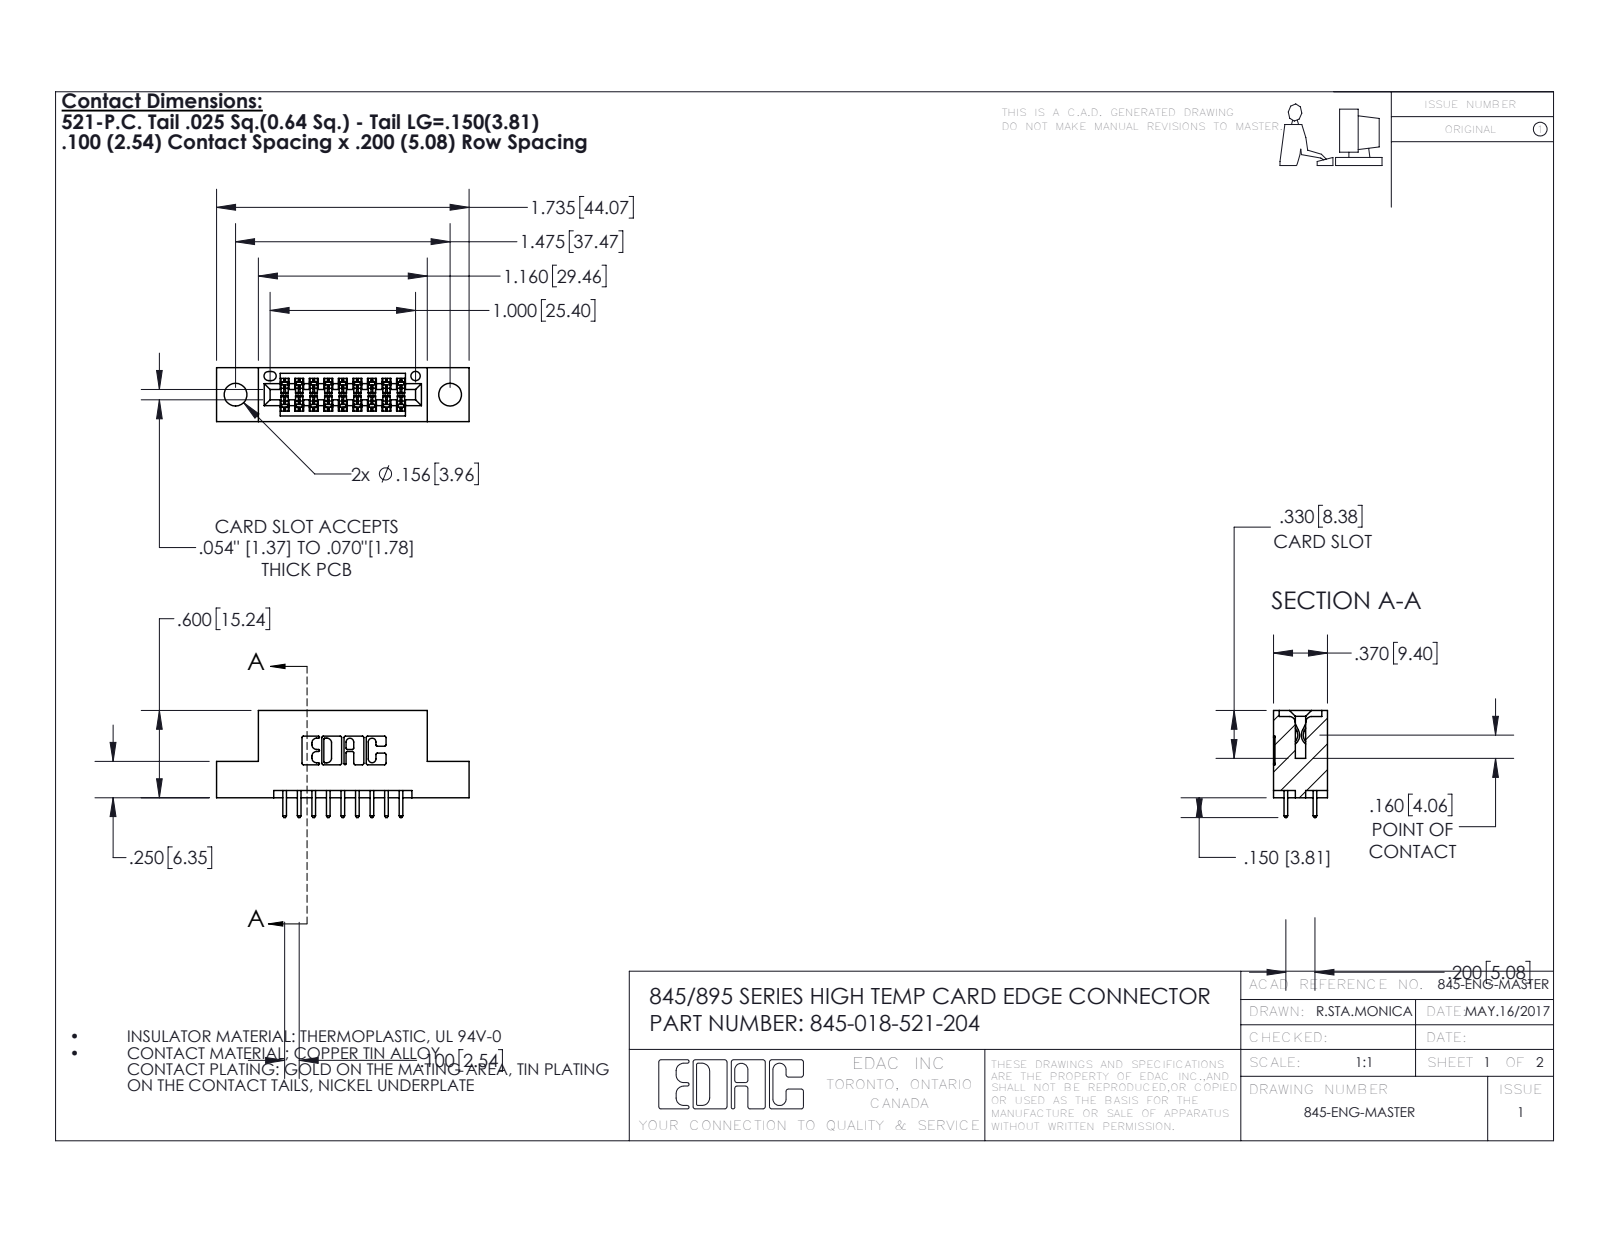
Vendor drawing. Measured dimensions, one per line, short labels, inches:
name: 345-292-001_345-293-121; 345-018-521-204; 345 Part_Flush Mounting Lugs - 0.156 Dia-TH
written by: SolidWorks 2016 (CONFIG_CONTROL_DESIGN)
unit: in
bodies: 19 solids, 1026 faces (674 planar, 352 cylindrical, 0 other)
size: 1.735 × 0.737 × 0.37
volume: 0.237 in³; area: 7.537 in²
holes: 2× ⌀0.156, 1× ⌀0.064
rounds: 27× R0.006, 22× R0.01, 18× R0.01, 6× R0.007, 6× R0.031, 3× R0.026, 2× R0.014, 2× R0.019
face distances: 0.2, 0.298, 0.072, 0.37, 0.1, 0.098, 0.272, 0.025, 0.225, 0.6
hole spacings: 0.27, 1.244, 1.475
